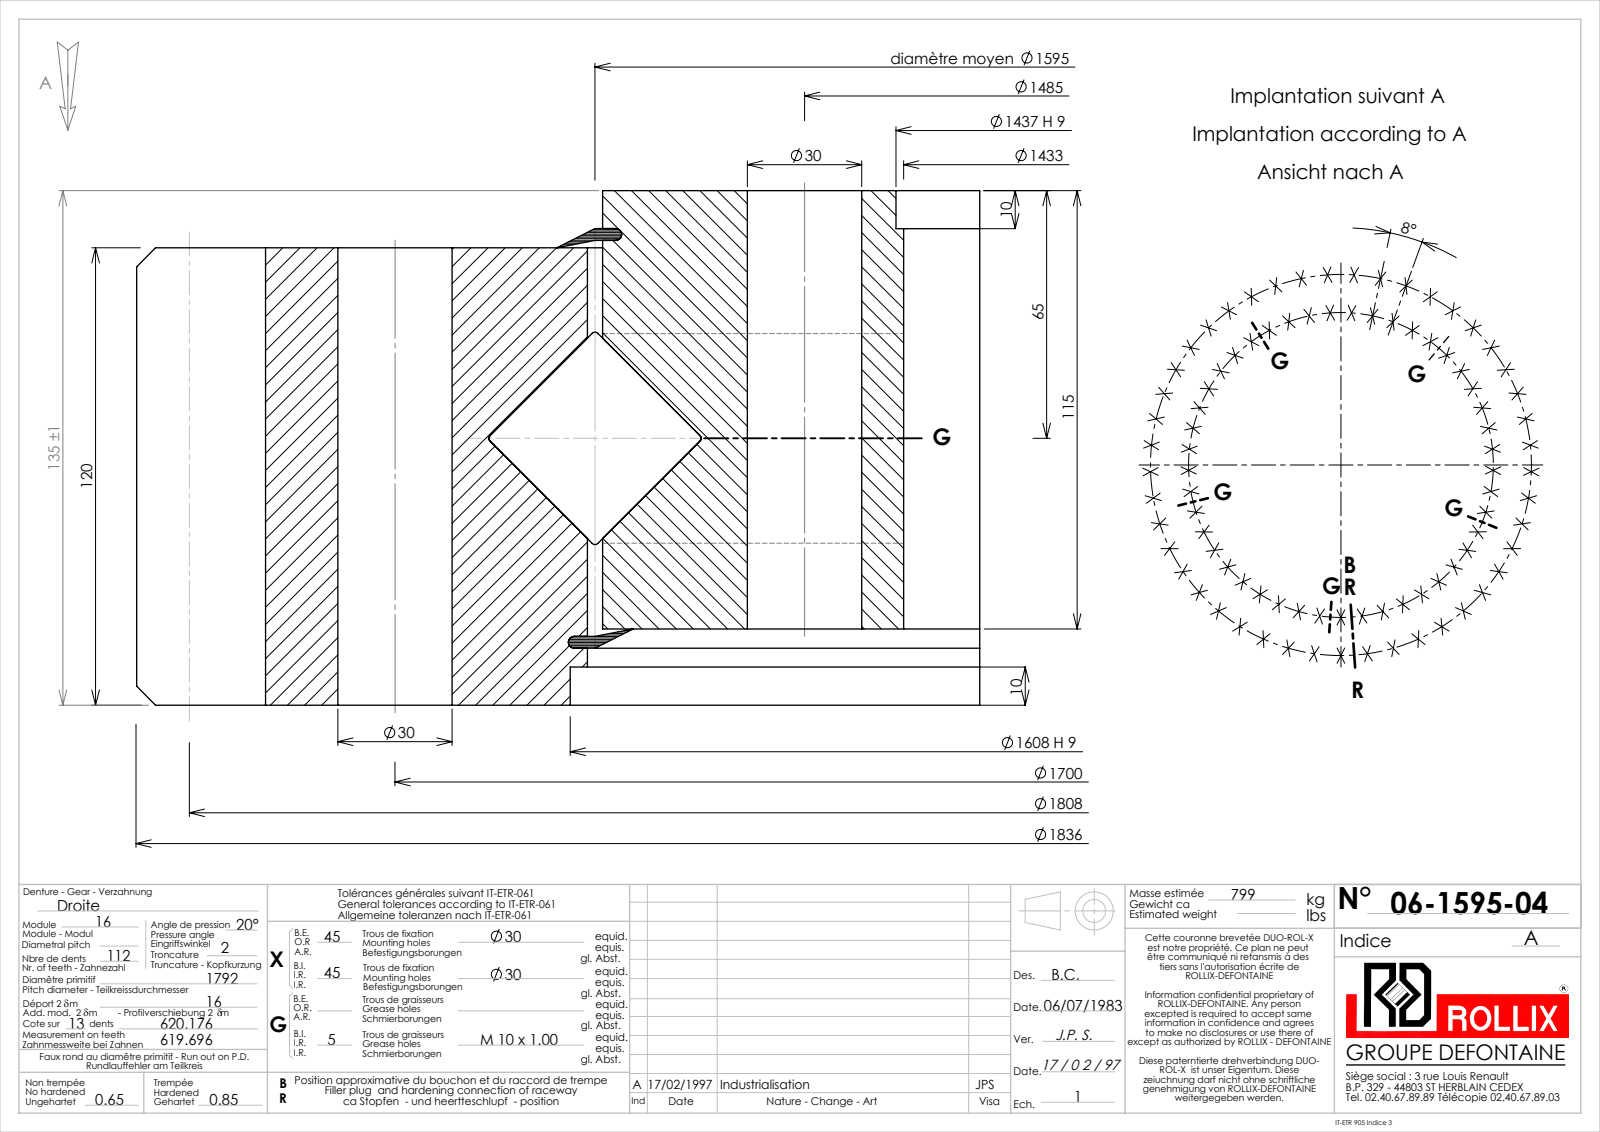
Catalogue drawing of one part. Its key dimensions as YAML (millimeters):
part_name: "06-1595-04"
step_written_by: "SolidWorks 2016 (CONFIG_CONTROL_DESIGN)"
units: millimeters
bodies: {solids: 5, faces: 945, planar: 240, cylindrical: 435, other: 270}
overall_size: [1835.66, 1835.66, 135]
volume: 94780000
surface_area: 6419000
round_holes:
  - {diameter: 30, count: 90}
  - {diameter: 9, count: 5}
  - {diameter: 1433, count: 1}
  - {diameter: 1437, count: 1}
  - {diameter: 1599, count: 1}
  - {diameter: 1608, count: 1}
round_bosses_or_shafts:
  - {diameter: 1591, count: 1}
  - {diameter: 40, count: 1}
partial_cylinders:
  - {radius: 884, count: 1}
  - {radius: 918, count: 1}
face_to_face_distances: [120, 115, 20, 100, 135, 15, 5.05, 105.05, 3.1, 1.95]
hole_center_spacings: [1092.74, 118.58, 353.45, 798.1, 236.59, 468.58, 691.45, 1180.92]
